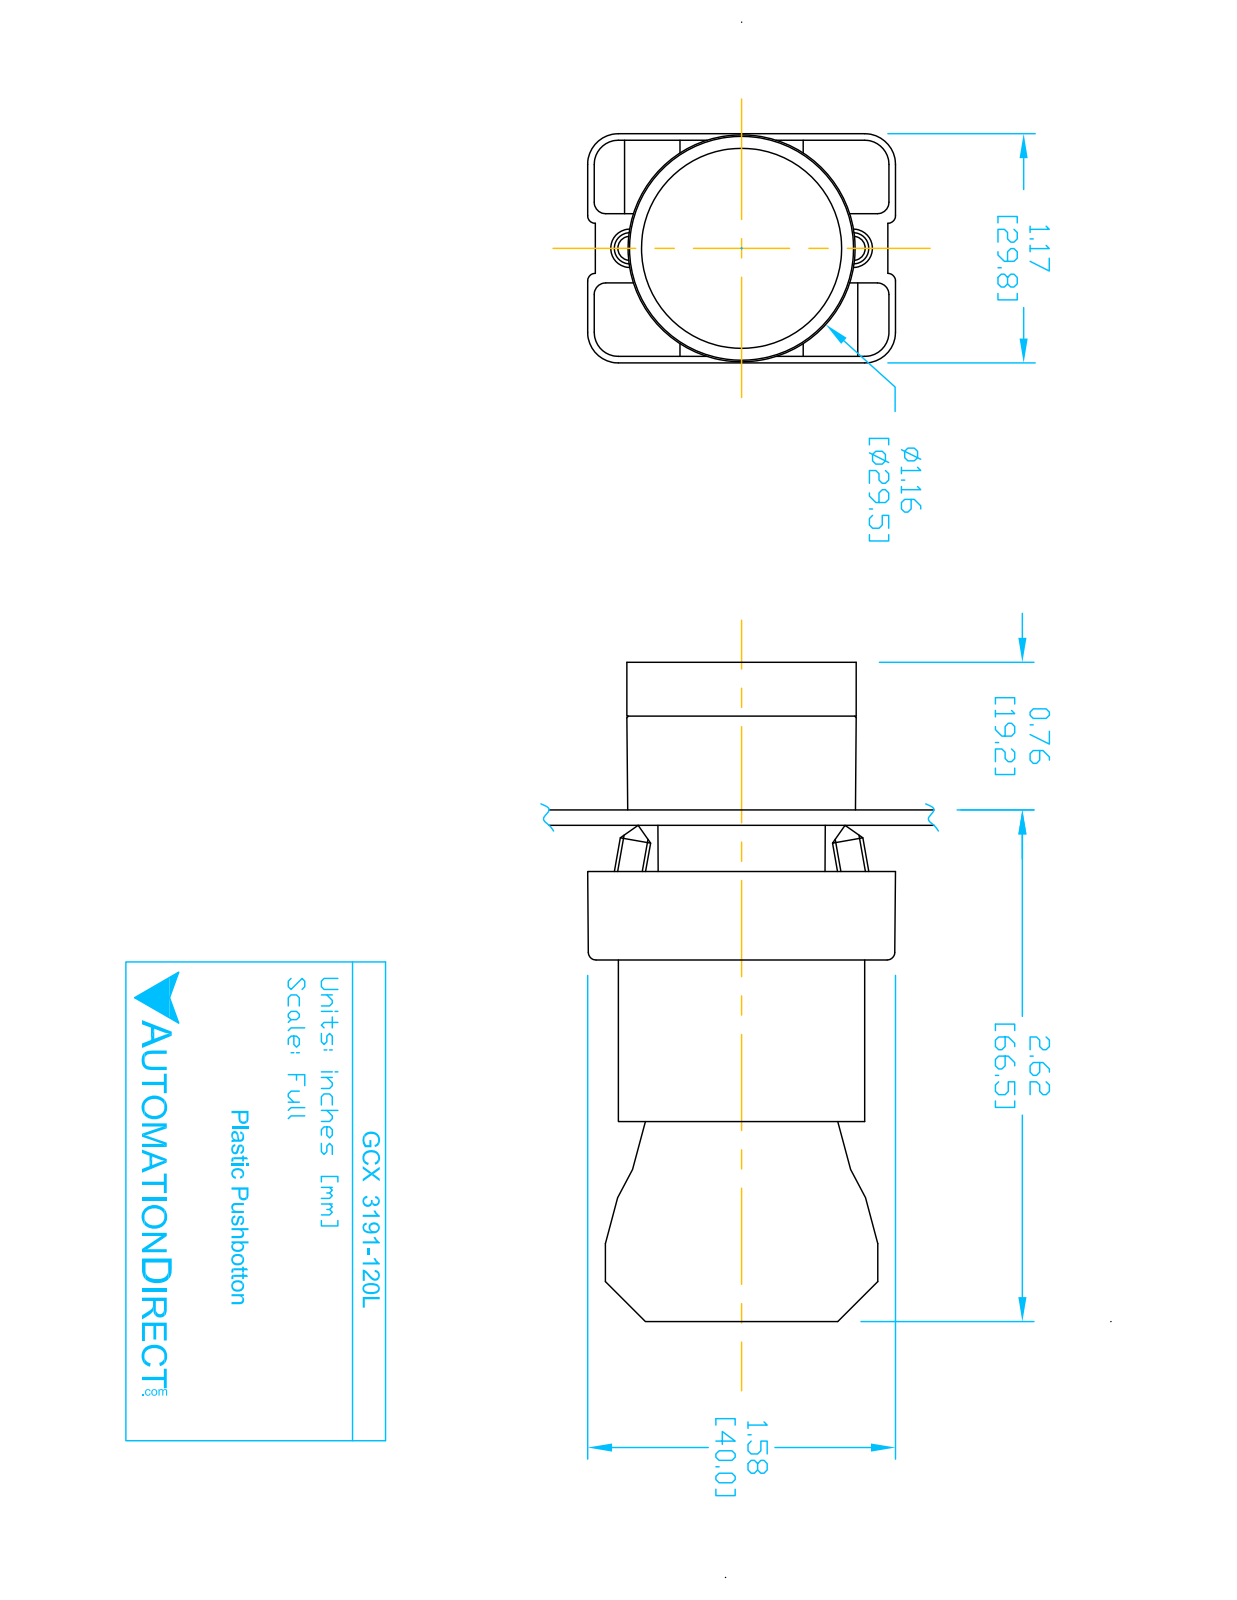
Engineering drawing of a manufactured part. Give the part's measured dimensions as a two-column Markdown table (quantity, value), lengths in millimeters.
| quantity | value |
| --- | --- |
| part name | ECX3029-2; CONTACT BLOCK; GCX3191L OPERATOR; GCX3191-120L (+1 more) |
| STEP written by | SolidWorks 2016 (AUTOMOTIVE_DESIGN) |
| units | millimeters |
| bodies | 8 solids, 431 faces (252 planar, 148 cylindrical, 31 other) |
| overall size | 84.3 × 40.2 × 29.9 |
| volume | 45 790 mm³ |
| surface area | 25 010 mm² |
| round holes (diameter × count) | 2 × 2, 3.1 × 2, 3.3 × 2, 2.2 × 1, 5 × 1, 11.9 × 1, 22.3 × 1, 22.6 × 1, 26 × 1 |
| round bosses / shafts (diameter × count) | 4 × 4, 29.8 × 1, 25.5 × 1, 24 × 1, 21.7 × 1, 19.8 × 1, 12.8 × 1 |
| partial cylindrical surfaces (radius × count) | 1.5 × 24, 1 × 12, 3.1 × 12, 4 × 12, 1 × 8, 3.3 × 2, 0.5 × 1, 1.6 × 1 |
| main face-to-face distances | 21, 14.7, 51.3, 30.3, 29.7, 7, 58.3, 37.3, 0.8, 0.8 |
| hole center spacings | 6, 13.8, 12, 12.4 |
